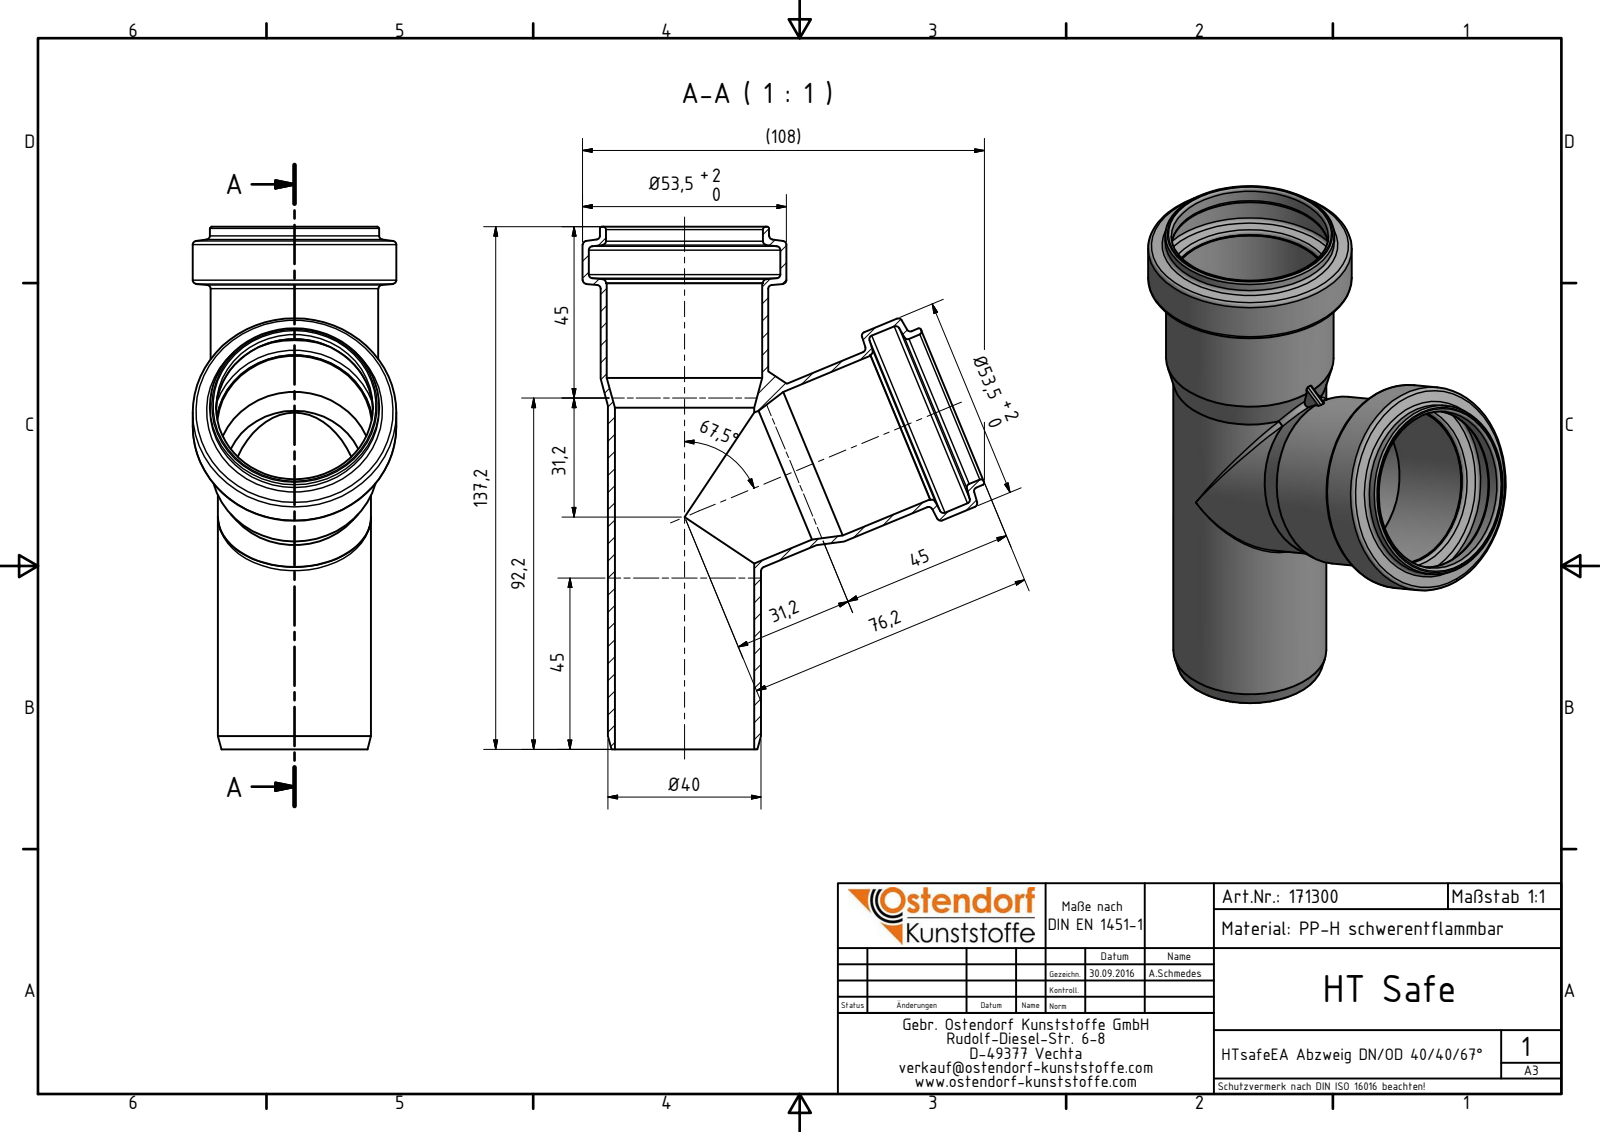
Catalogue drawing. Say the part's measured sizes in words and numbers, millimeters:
The part is named "171300 HTsafeEA DN_OD 40_40_67°". Its 3-D file was written by "Autodesk Inventor 2016 (AUTOMOTIVE_DESIGN)". It is 1 solid with 66 faces: 8 planar, 20 cylindrical and 38 other. Overall it measures 137.2 by 105.49 by 53.5 millimeters. Its volume is 44 884 cubic millimeters and its surface area 53 173 square millimeters. Round holes: 3 of diameter 41.2, 2 of diameter 36.6, 2 of diameter 40.8, 2 of diameter 50.3. Round bosses or shafts: 2 of diameter 53.5, 2 of diameter 44.4, 2 of diameter 44, 2 of diameter 40.2. Partial cylindrical surfaces (rounded edges, fillets, slot ends): 2 of radius 0.5. The main face-to-face distances are 14.9, 137.2, 122.3, 1.9.
